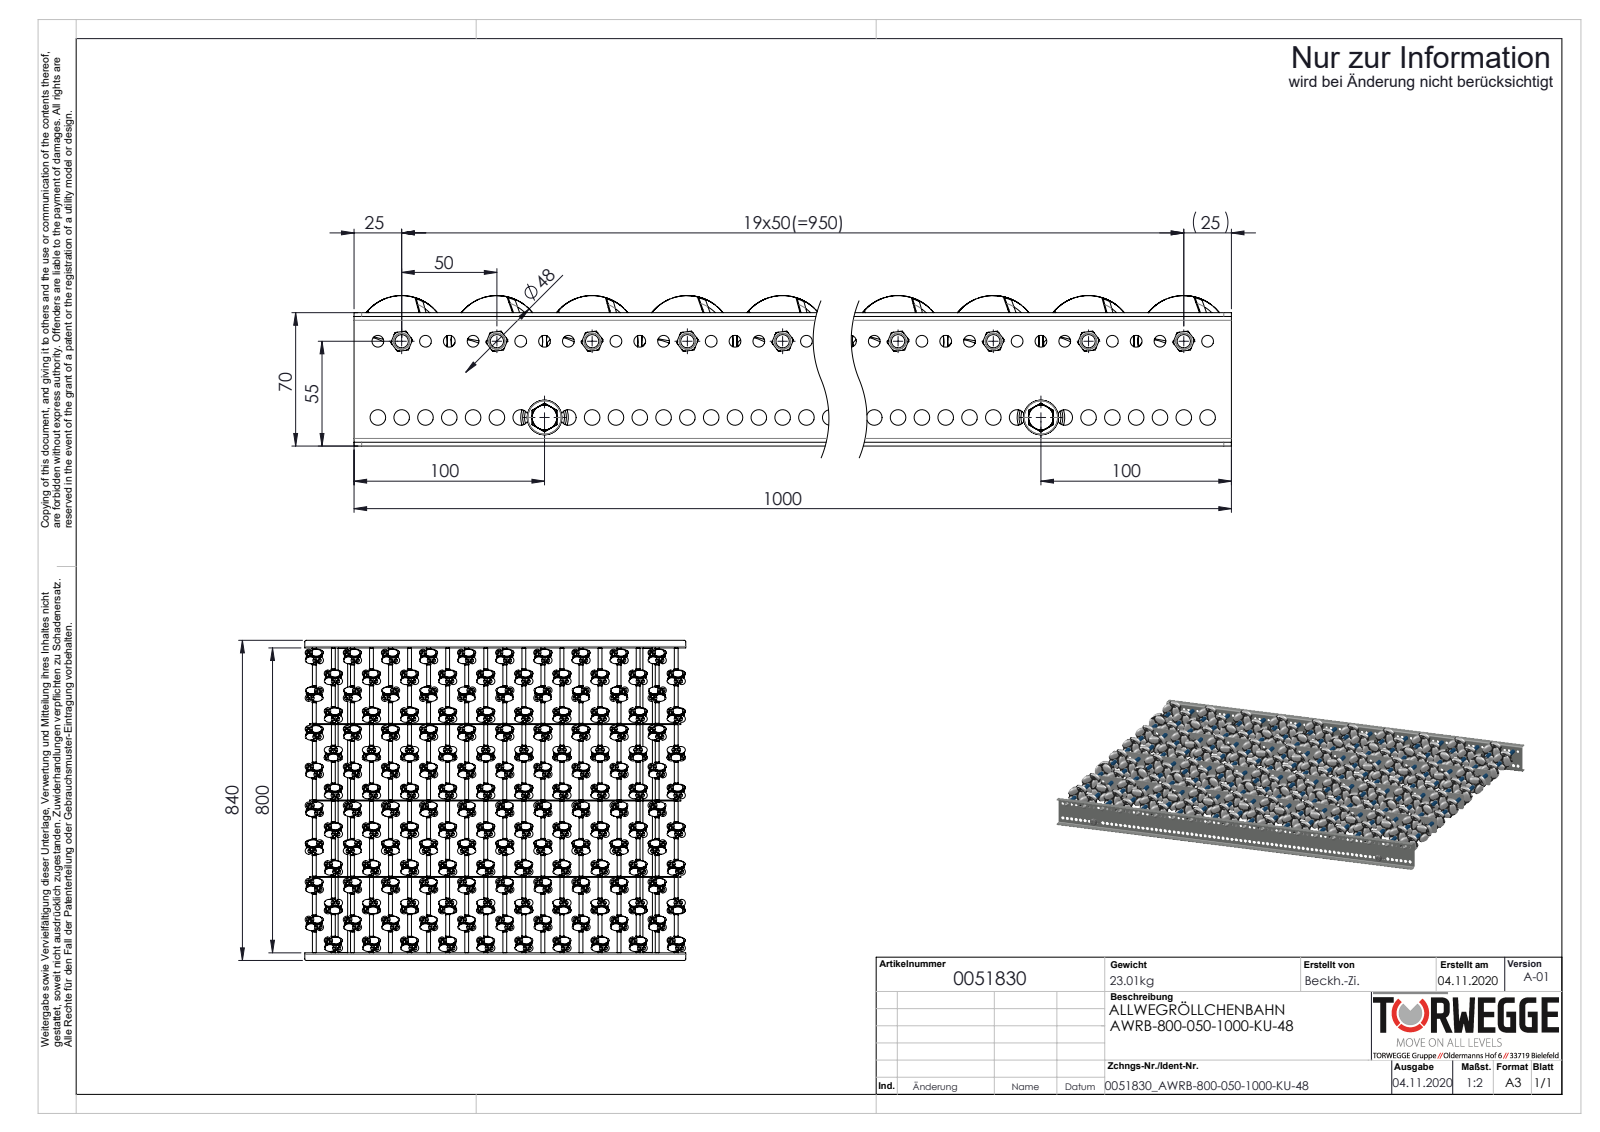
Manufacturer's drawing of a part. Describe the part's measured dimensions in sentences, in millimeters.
The part is named "Traversen_KFG_L800; 0051830; 0019719_Gewindestange-M6_L=820; S108767_Längstraverse-42x2,5-AWR_L1000 (+8 more)". Its 3-D file was written by "SolidWorks 2020 (AUTOMOTIVE_DESIGN)". It is 2635 solids with 46016 faces: 16178 planar, 17774 cylindrical and 12064 other. Overall it measures 1000 by 840 by 79 millimeters. Its volume is 8 605 000 cubic millimeters and its surface area 5 734 000 square millimeters. Round holes: 960 of diameter 3.7, 960 of diameter 4.2, 79 of diameter 6.2, 79 of diameter 8.2, 39 of diameter 6.5, 20 of diameter 4.92, 20 of diameter 8.4, 2 of diameter 6.8, 2 of diameter 21. Round bosses or shafts: 960 of diameter 4, 839 of diameter 3.7, 22 of diameter 8, 20 of diameter 47.1, 20 of diameter 42, 20 of diameter 11, 20 of diameter 10, 20 of diameter 7. Partial cylindrical surfaces (rounded edges, fillets, slot ends): 8 of radius 4, 4 of radius 2, 4 of radius 5. The main face-to-face distances are 2, 200.5, 2.5, 802, 401, 203, 198, 68, 800, 804. The hole center spacings are 36.06, 36.05, 99, 36.07, 100, 36.04, 50, 122.72.
